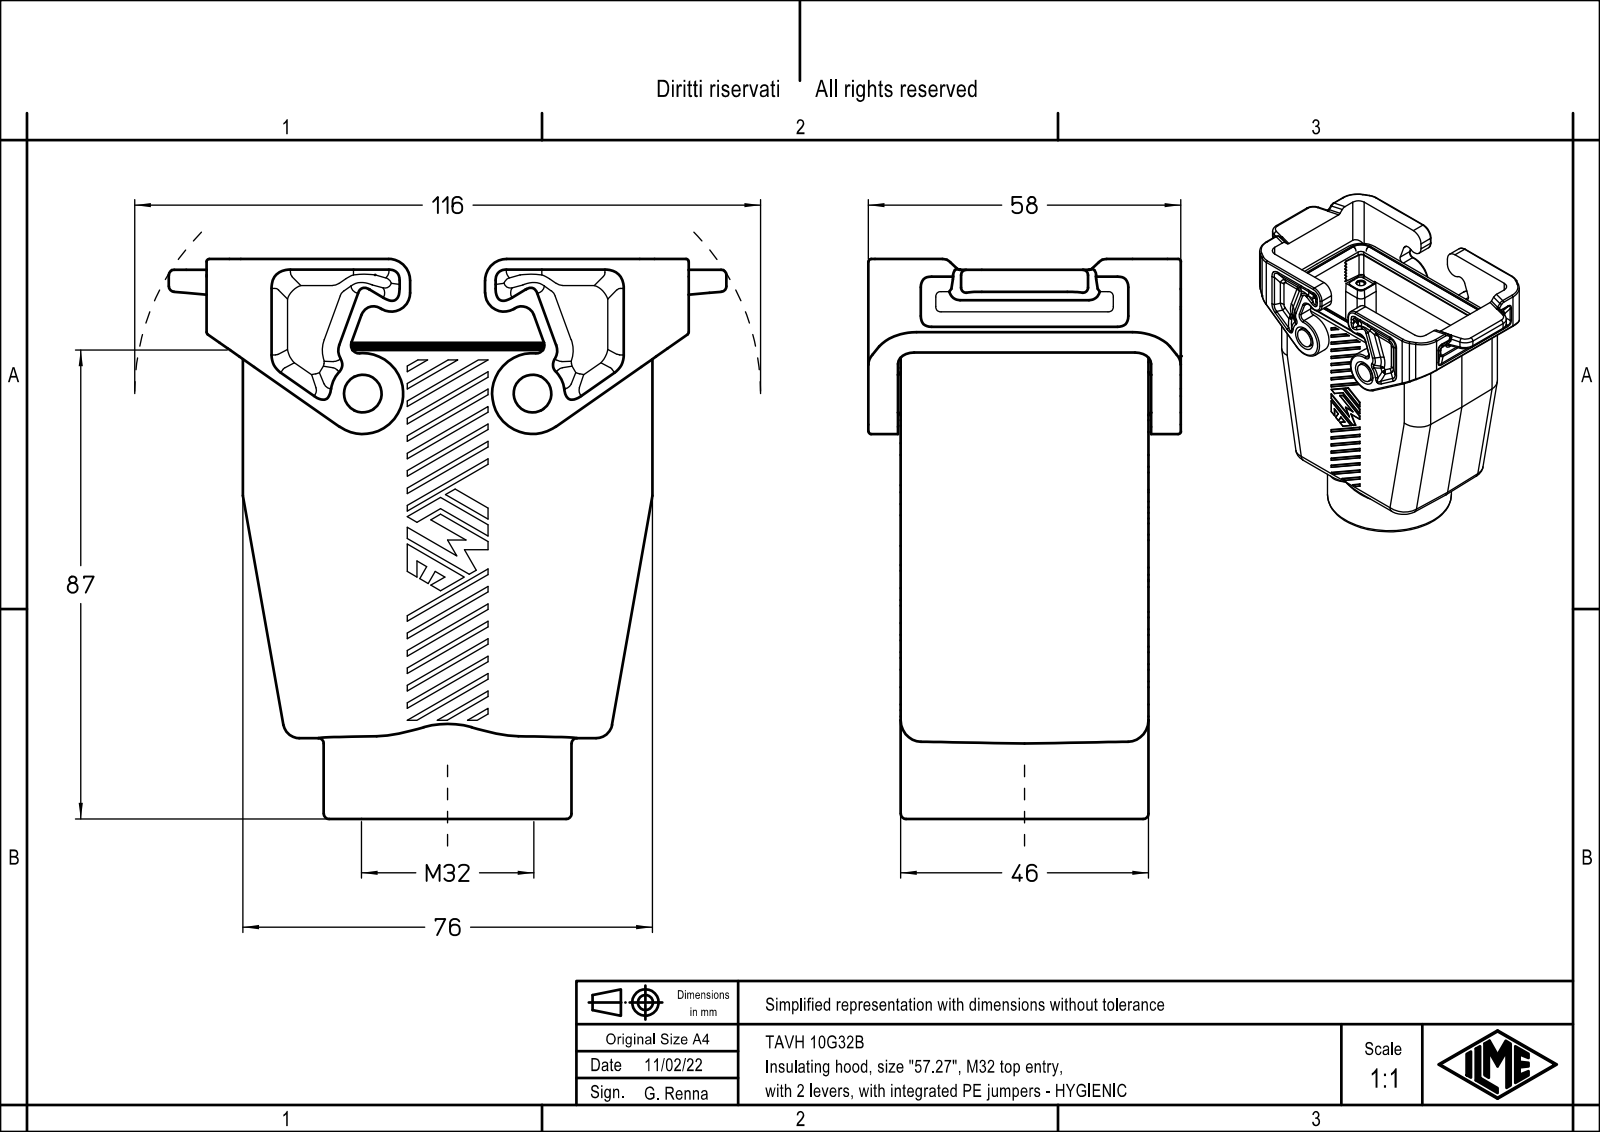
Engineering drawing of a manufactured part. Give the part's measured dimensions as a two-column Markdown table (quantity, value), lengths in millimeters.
| quantity | value |
| --- | --- |
| part name | TAVH 10 G32 |
| STEP written by | Creo Elements/Direct Modeling 20.1B 02-Apr-2019 (C) Parametric Technology GmbH (AUTOMOTIVE_DESIGN) |
| units | millimeters |
| bodies | 1 solid, 856 faces (396 planar, 398 cylindrical, 62 other) |
| overall size | 103.9 × 103.5 × 58 |
| volume | 134 119 mm³ |
| surface area | 54 094 mm² |
| round holes (diameter × count) | 3.5 × 4, 28 × 1, 30.6 × 1 |
| round bosses / shafts (diameter × count) | 7 × 2, 46 × 1 |
| partial cylindrical surfaces (radius × count) | 0.15 × 128, 2 × 20, 3 × 20, 1.5 × 18, 1 × 16, 1.3 × 12, 6 × 8, 7 × 8 |
| main face-to-face distances | 5.4, 40.6, 46, 35.2, 0.5, 5.9, 41.1, 46.5, 5.5, 52.5 |
| hole center spacings | 31.54, 27, 57, 63.07 |
